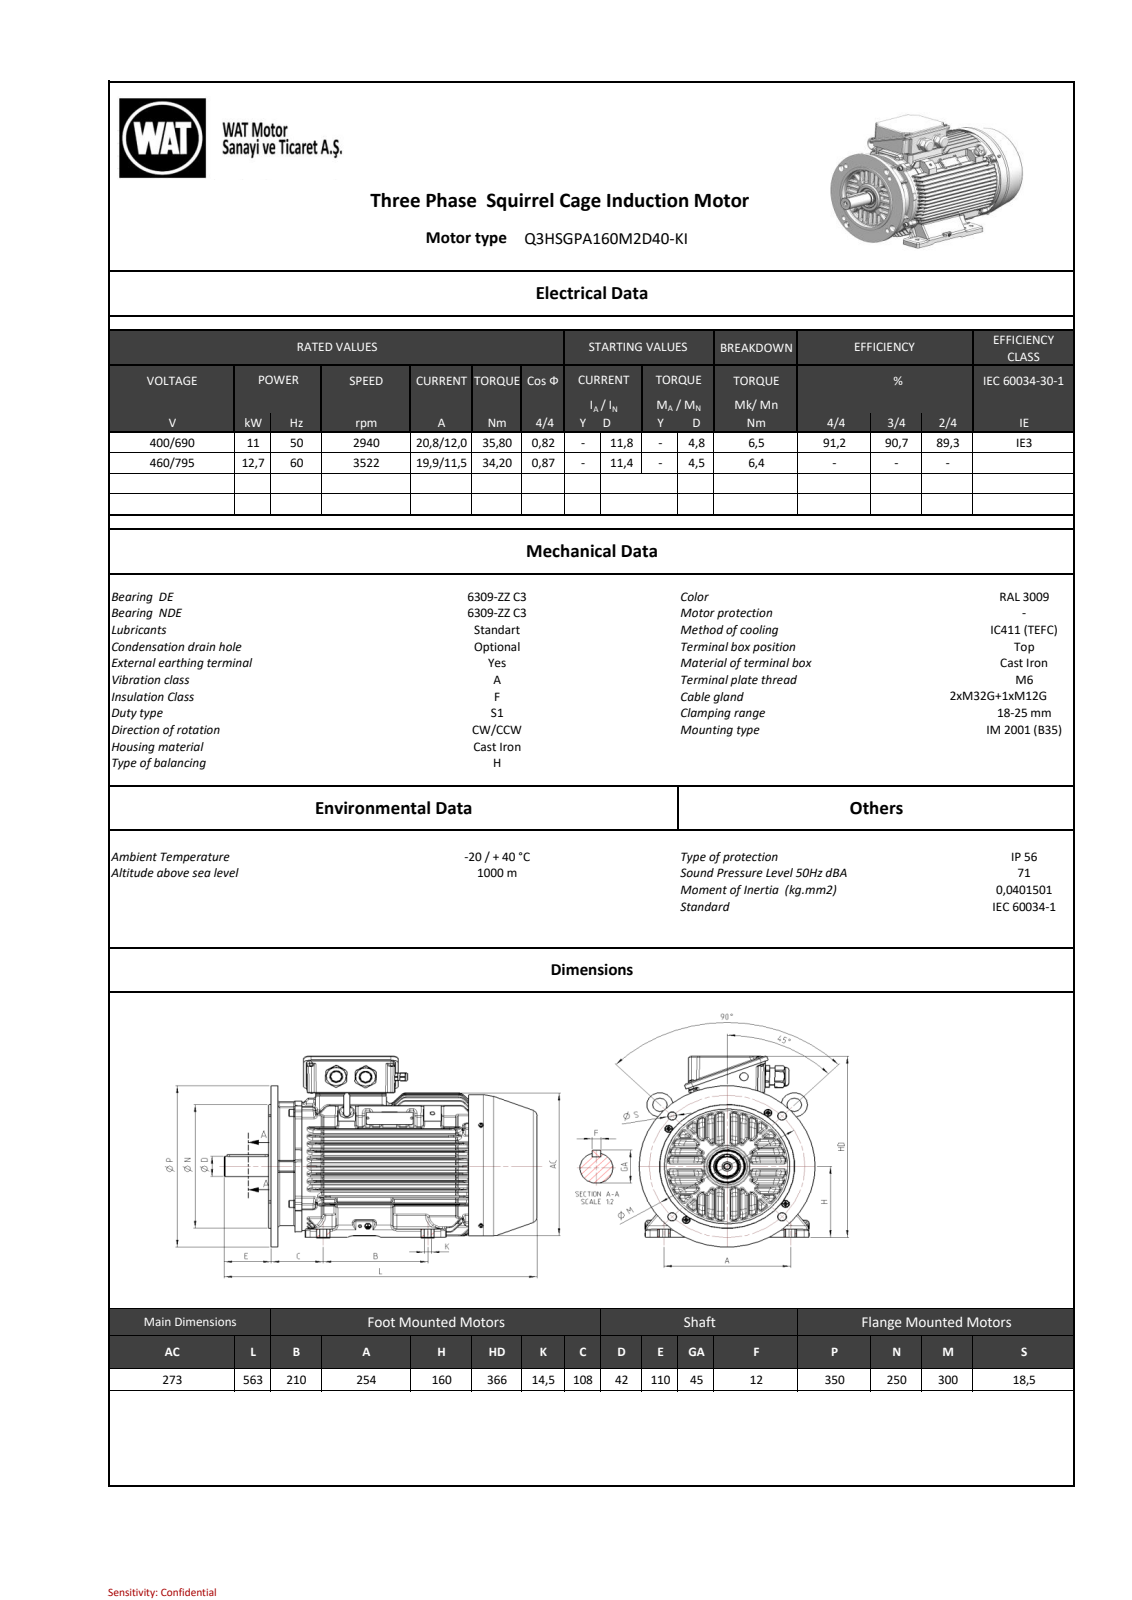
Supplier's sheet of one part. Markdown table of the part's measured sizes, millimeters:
| quantity | value |
| --- | --- |
| part name | 26000C948E142sj1 |
| STEP written by | SIEMENS PLM Software NX 11.0 (AUTOMOTIVE_DESIGN) |
| units | millimeters |
| bodies | 0 solids, 6927 faces (1287 planar, 1872 cylindrical, 3768 other) |
| overall size | 563 × 380.49 × 349 |
| round holes (diameter × count) | 6.8 × 8, 15 × 4, 8.5 × 2, 13 × 2, 19 × 2, 21 × 2, 2.5 × 1, 4.2 × 1, 6 × 1, 11.3 × 1, 68.67 × 1, 180 × 1 |
| round bosses / shafts (diameter × count) | 10 × 4, 8.65 × 4, 8 × 4, 5 × 4, 36 × 2, 34.5 × 2, 31.25 × 2, 25 × 2 |
| partial cylindrical surfaces (radius × count) | 3 × 223, 4.5 × 212, 1.5 × 106, 4 × 100, 2 × 65, 1.8 × 64, 6 × 54, 28 × 24 |
| main face-to-face distances | 13.76, 13.83, 27.59, 27.73, 13.9, 41.49, 55.44, 41.68, 27.85, 13.95 |
| hole center spacings | 121.5, 171.83, 42.2, 139.38, 199.06, 239.31, 243.01, 35.5 |
